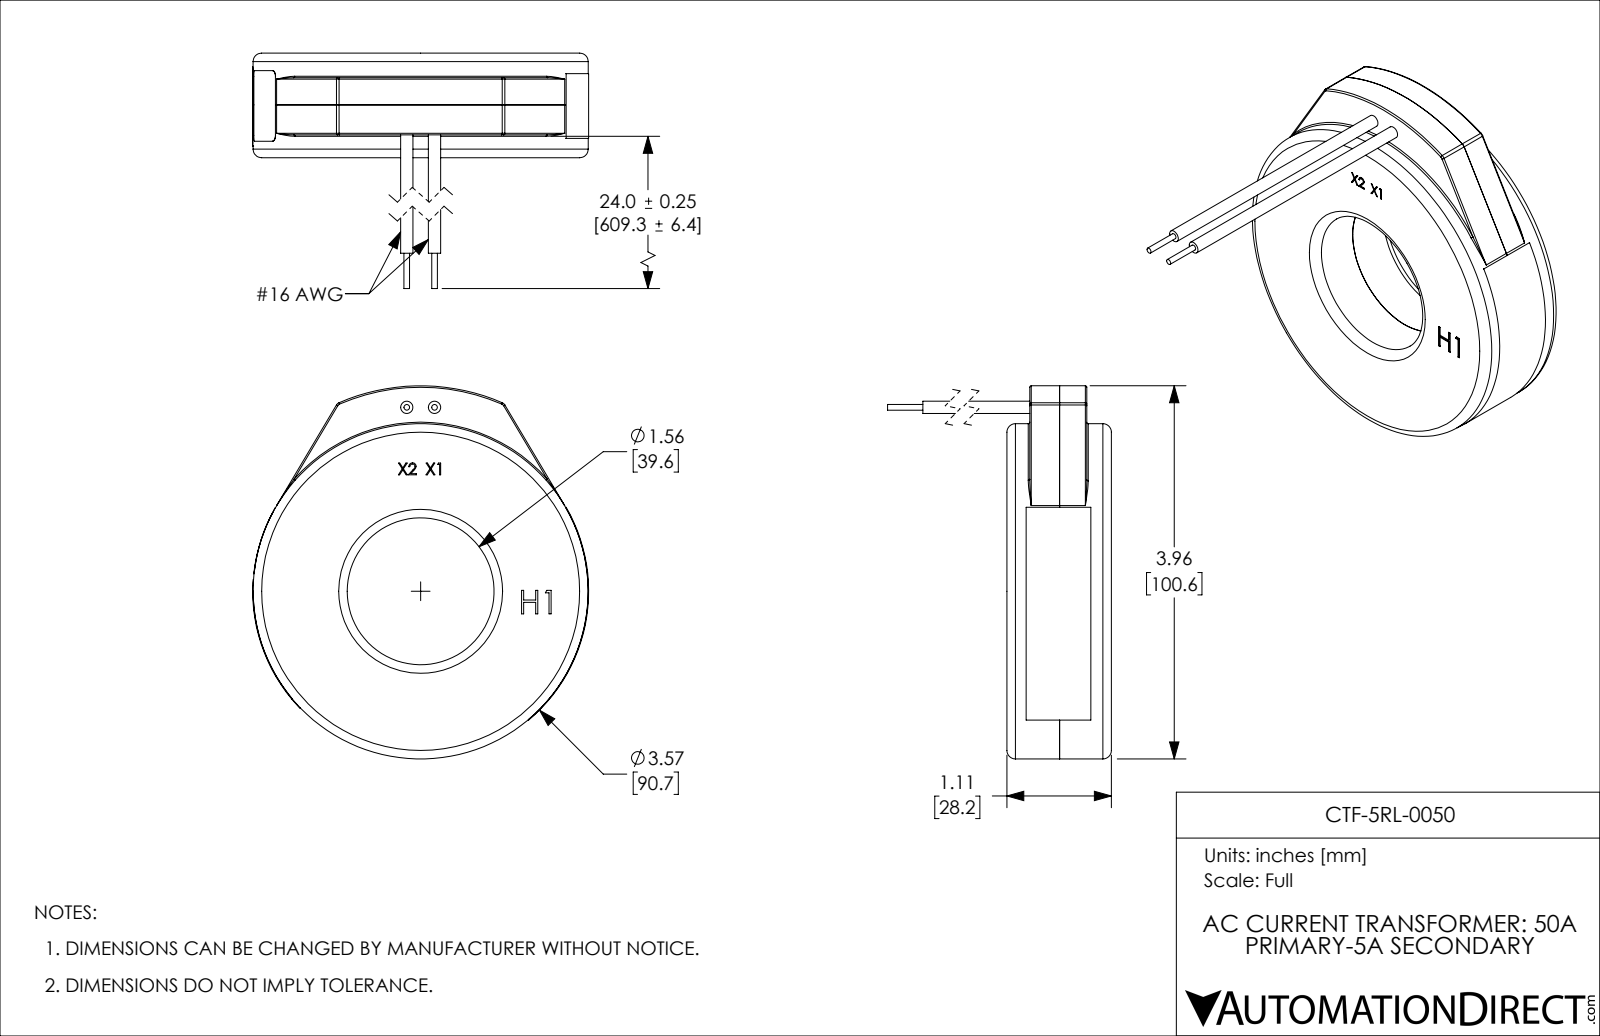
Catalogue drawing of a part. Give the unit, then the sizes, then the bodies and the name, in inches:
Units: inches
Overall size (bounding box): 4.242 × 3.962 × 3.57
Round holes (diameter × count): ⌀1.56 ×1
Round bosses / shafts (diameter × count): ⌀0.13 ×2, ⌀0.06 ×2, ⌀3.56 ×1
Partial cylindrical surfaces — rounded edges, fillets, slot ends (radius × count): R0.125 ×3, R0.015 ×2, R0.016 ×2, R0.06 ×2, R1.779 ×1, R1.782 ×1, R1.785 ×1, R2.182 ×1
Main face-to-face distances: 0.55, 1.11, 0.56, 0.867, 0.317, 0.243, 0.261, 0.289, 0.606, 0.849
Volume: 9.55 in³ · Surface area: 62.68 in²
Bodies: 7 solids, 154 faces (87 planar, 37 cylindrical, 30 other)
Part name (STEP PRODUCT): CTF-5RL-0050
STEP written by: SolidWorks 2018 (AUTOMOTIVE_DESIGN)
